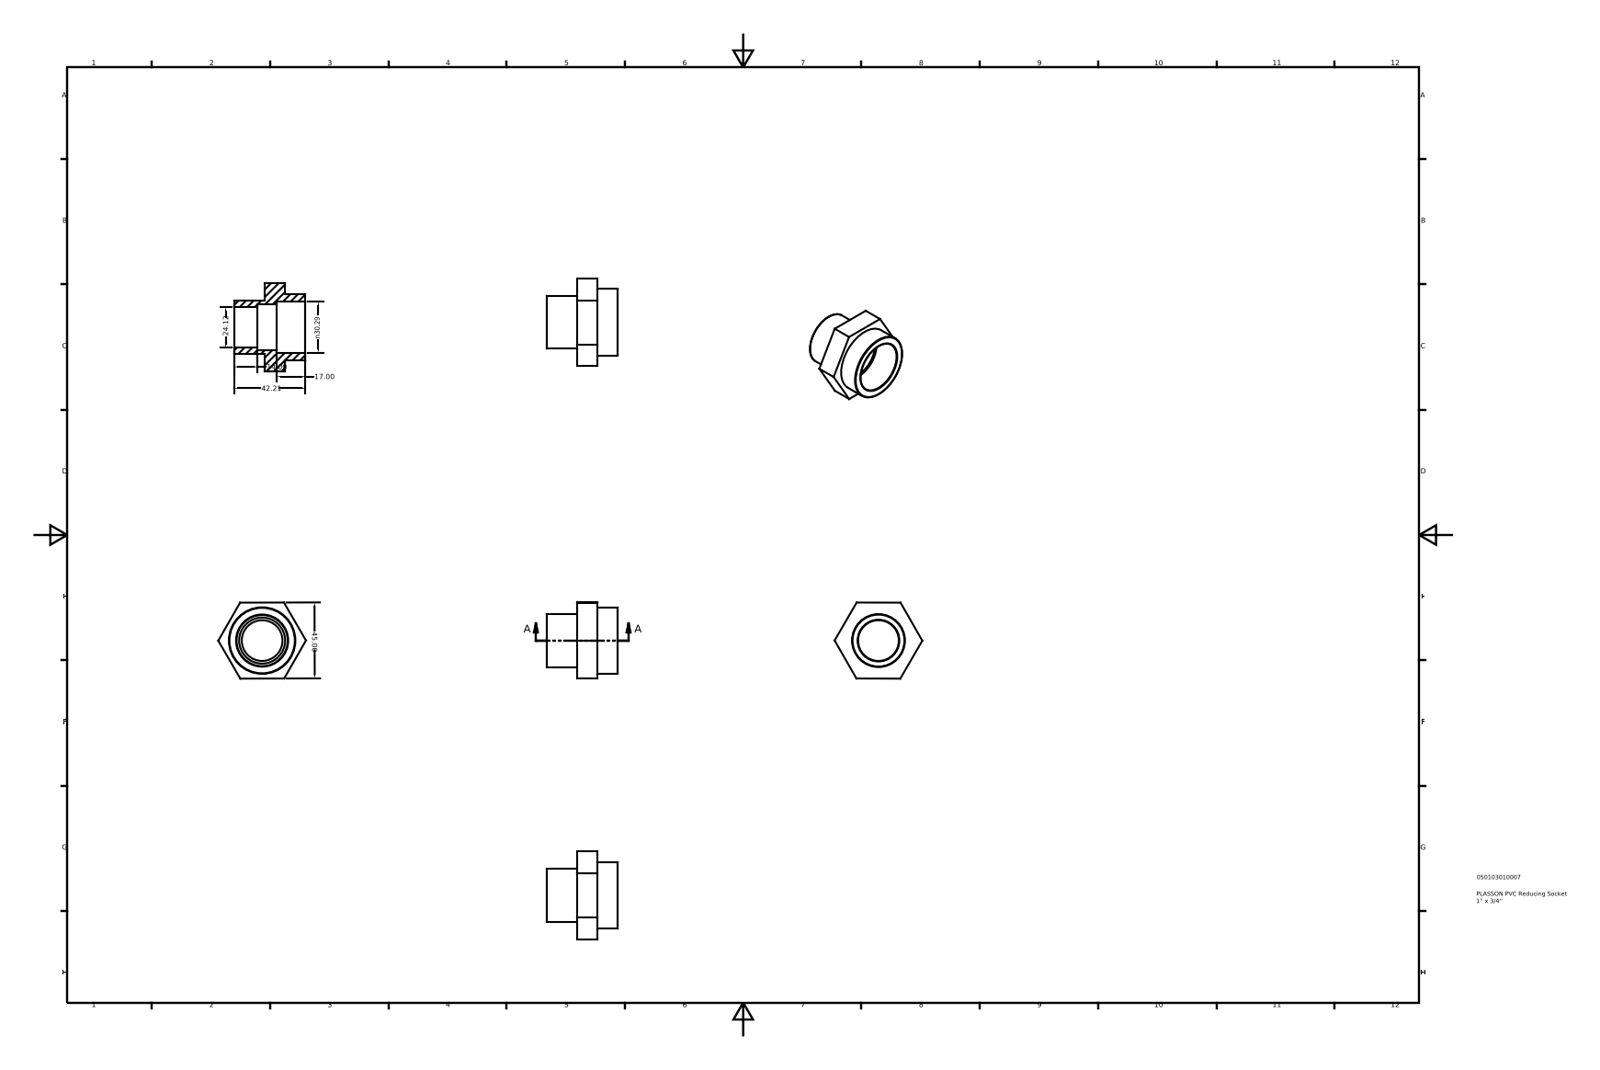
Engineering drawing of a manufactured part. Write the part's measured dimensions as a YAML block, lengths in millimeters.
part_name: "050103010007"
step_written_by: "Autodesk Inventor 2015 (AUTOMOTIVE_DESIGN)"
units: millimeters
bodies: {solids: 1, faces: 21, planar: 12, cylindrical: 5, other: 4}
overall_size: [51.96, 45.08, 42.21]
volume: 24475
surface_area: 11327
round_holes:
  - {diameter: 24.12, count: 1}
  - {diameter: 27.26, count: 1}
  - {diameter: 30.29, count: 1}
round_bosses_or_shafts:
  - {diameter: 39.38, count: 1}
  - {diameter: 31.35, count: 1}
face_to_face_distances: [44.98, 12, 23.9, 11.9, 45, 18.32, 30.32, 42.22, 25.22, 6.9]
